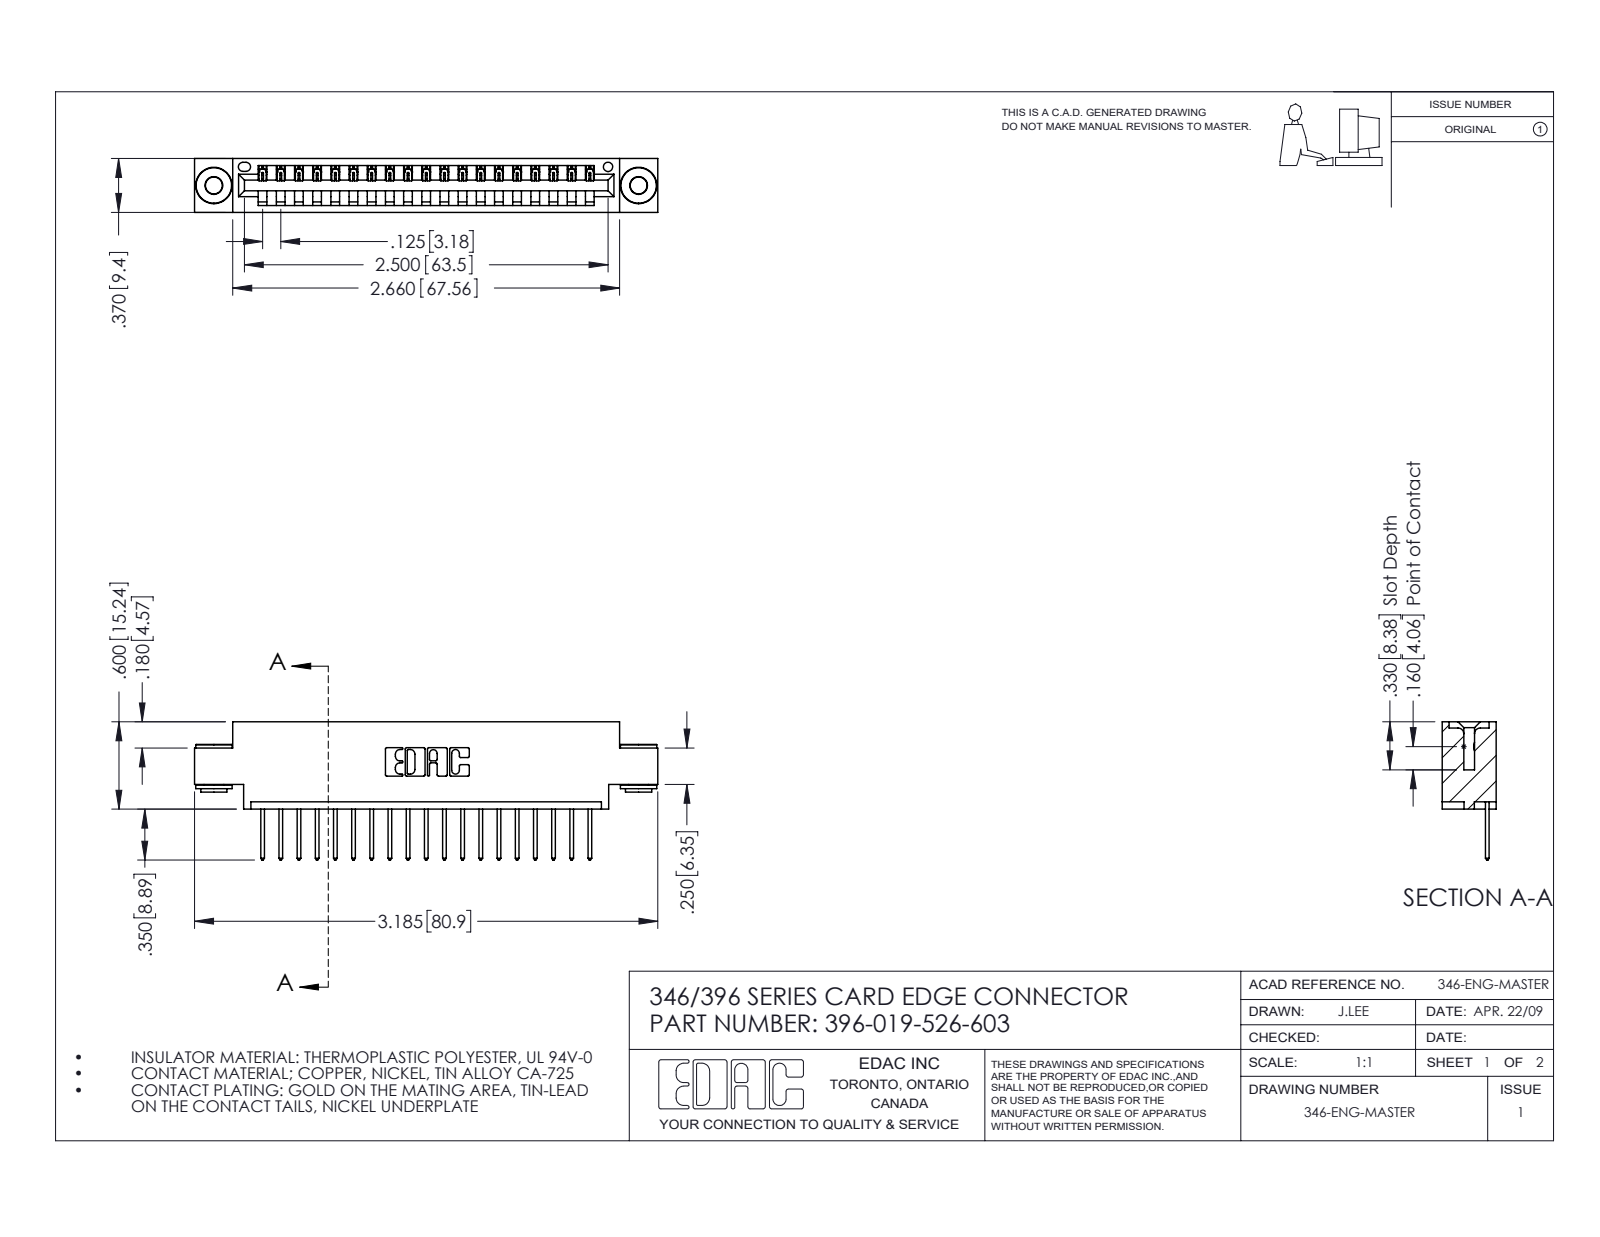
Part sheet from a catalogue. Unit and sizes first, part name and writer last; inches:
Units: inches
Overall size (bounding box): 3.185 × 0.95 × 0.37
Round holes (diameter × count): ⌀0.116 ×2, ⌀0.156 ×2, ⌀0.064 ×1
Round bosses / shafts (diameter × count): ⌀0.25 ×2, ⌀0.18 ×2, ⌀0.136 ×2
Partial cylindrical surfaces — rounded edges, fillets, slot ends (radius × count): R0.006 ×38, R0.01 ×38, R0.01 ×22, R0.007 ×6, R0.031 ×6, R0.026 ×3, R0.031 ×2, R0.04 ×2
Main face-to-face distances: 0.048, 0.322, 0.37, 0.25, 0.025, 0.072, 0.298, 0.148, 0.222, 0.1
Hole centre spacings: 0.246, 2.713, 2.92
Volume: 0.454 in³ · Surface area: 14.58 in²
Bodies: 22 solids, 1266 faces (850 planar, 408 cylindrical, 8 other)
Part name (STEP PRODUCT): 345-250-002_345-250-002-102; 346 Part_0.170 Offset - 0.156 Dia-TH; 396-019-526-603; 345-292-001_345-293-126
STEP written by: SolidWorks 2016 (CONFIG_CONTROL_DESIGN)
